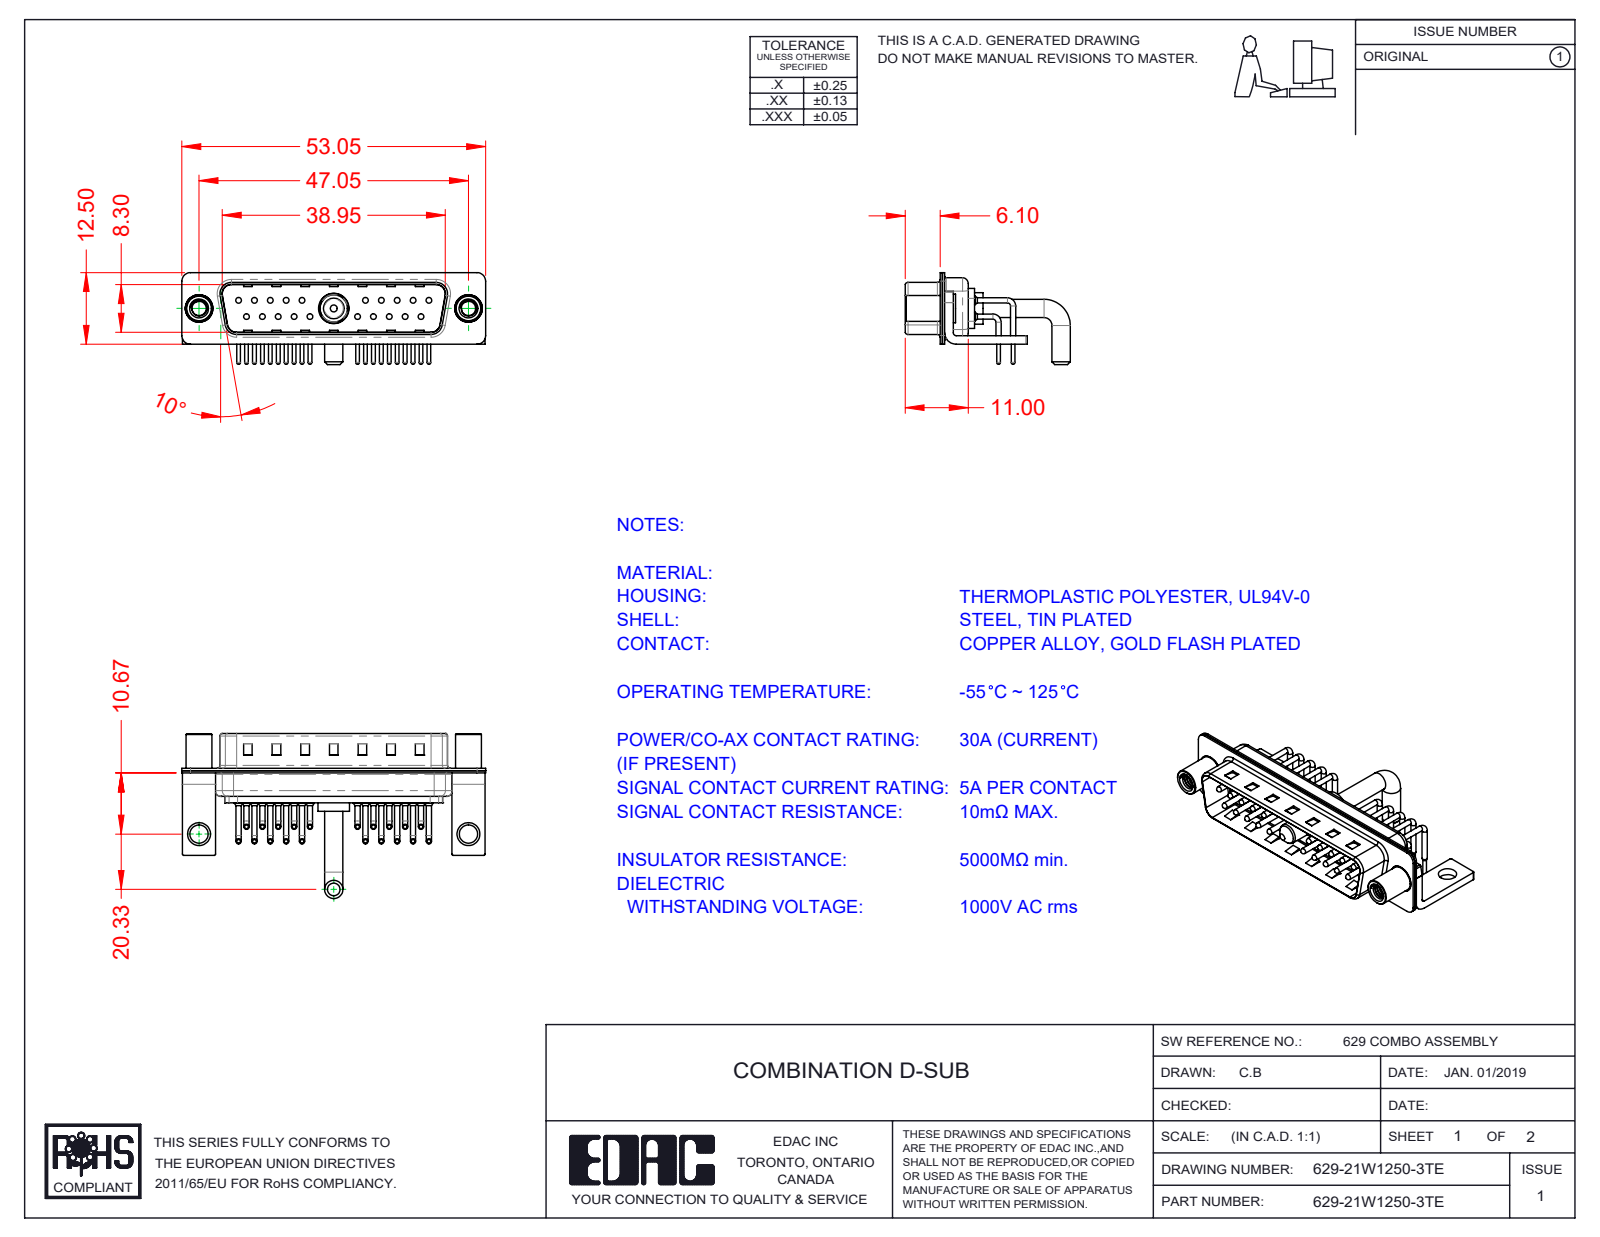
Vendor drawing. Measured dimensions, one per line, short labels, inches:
name: 629-21W1250-3TE; 629Combo Contact Row 2; 629Combo Contact Row 1; 629Combo Threaded Standoff_D (+5 more)
written by: SolidWorks 2020 (CONFIG_CONTROL_DESIGN)
unit: in
bodies: 29 solids, 2717 faces (1483 planar, 950 cylindrical, 284 other)
size: 2.089 × 1.135 × 0.632
volume: 0.213 in³; area: 13.35 in²
holes: 20× ⌀0.03, 20× ⌀0.063, 20× ⌀0.079, 2× ⌀0.098, 2× ⌀0.126, 2× ⌀0.157, 2× ⌀0.189, 1× ⌀0.191, 1× ⌀0.209
bosses: 40× ⌀0.035, 20× ⌀0.059, 20× ⌀0.039, 20× ⌀0.026, 2× ⌀0.197, 2× ⌀0.193, 2× ⌀0.177, 2× ⌀0.126
rounds: 20× R0.04, 16× R0.01, 16× R0.059, 13× R0.079, 9× R0.02, 8× R0.063, 4× R0.024, 4× R0.026
face distances: 0.016, 0.031, 0.374, 0.059, 0.358, 0.343, 0.39, 0.024, 0.083, 0.03
hole spacings: 0.124, 0.109, 0.218, 0.327, 0.198, 0.763, 0.826, 0.872
